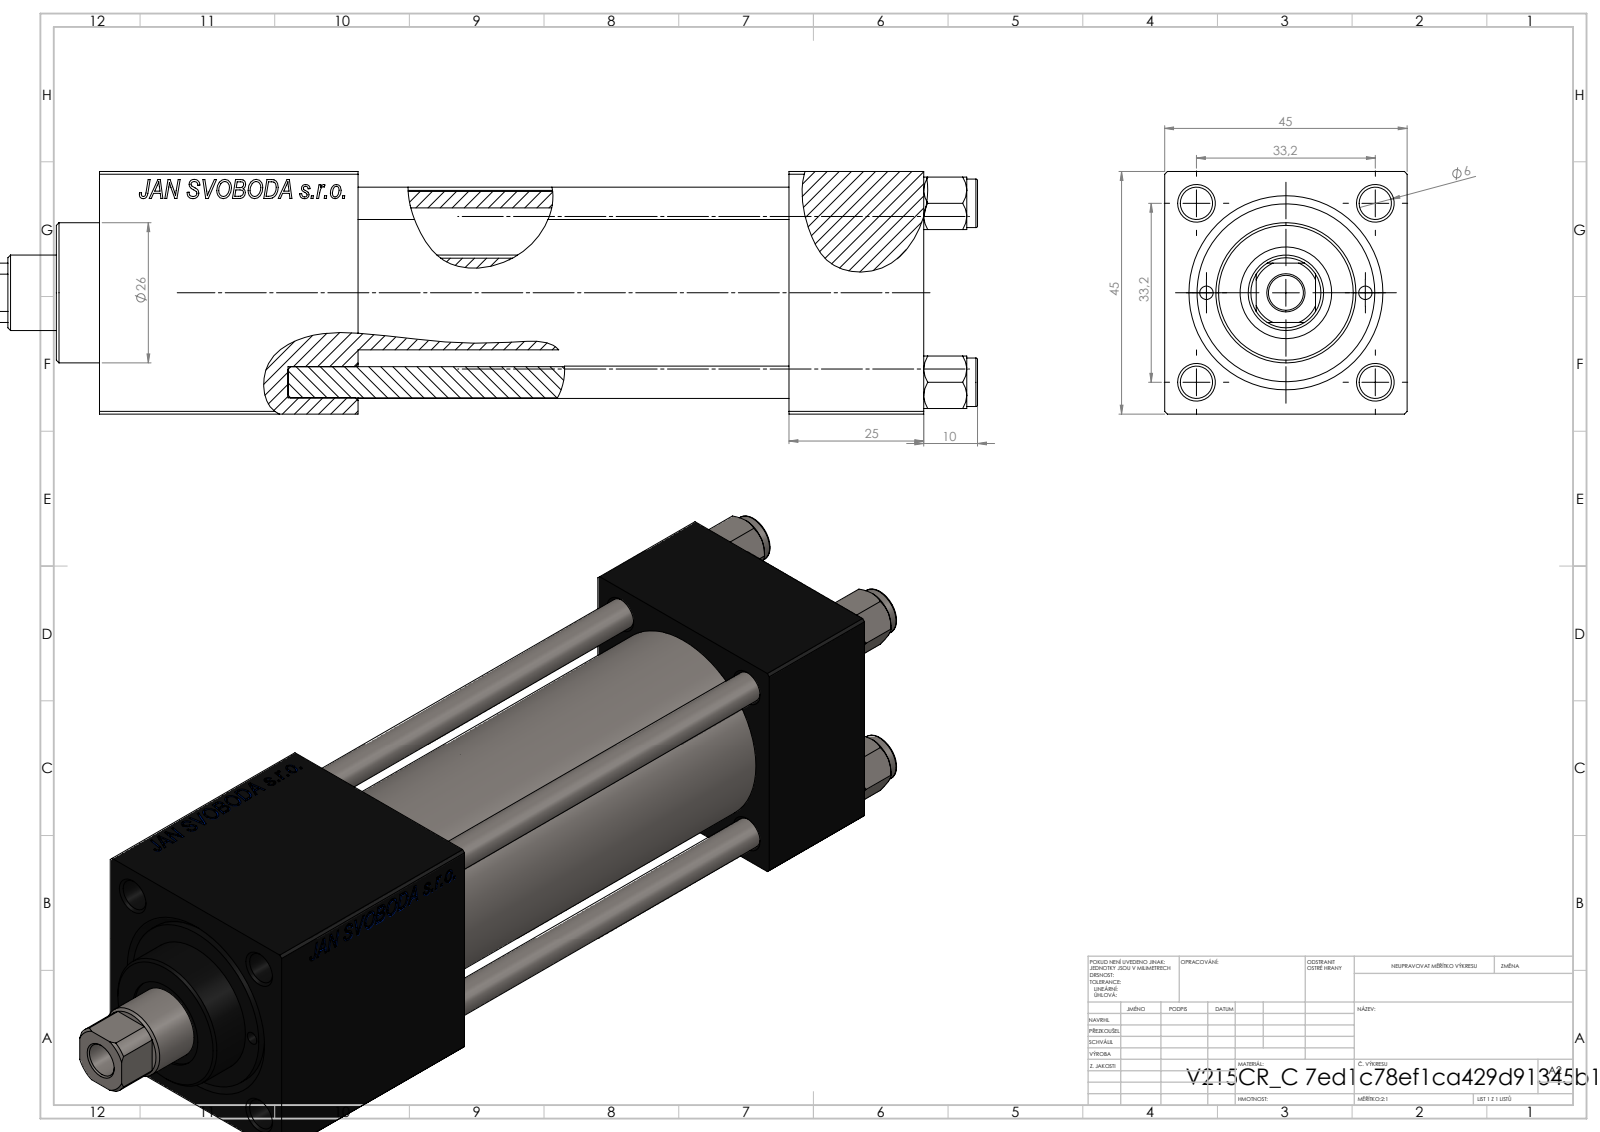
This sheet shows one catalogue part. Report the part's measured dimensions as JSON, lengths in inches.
{"part_name": "V215CR_C_Body; NUT_M5_C; V215CR_VCP_C; V215CR_C_TYCINKA (+1 more)", "step_written_by": "SolidWorks 2019 (CONFIG_CONTROL_DESIGN)", "units": "inches", "bodies": {"solids": 11, "faces": 1153, "planar": 527, "cylindrical": 90, "other": 536}, "overall_size": [7.402, 1.772, 1.772], "volume_in3": 12.92, "surface_area_in2": 119.9, "round_holes": [[0.236, 4], [0.098, 2], [0.276, 2], [0.518, 2], [0.787, 2], [0.256, 1], [0.551, 1], [0.669, 1], [0.945, 1], [1.26, 1], [1.299, 1]], "round_bosses_or_shafts": [[0.354, 4], [1.496, 1], [1.024, 1]], "partial_cylinders_radius": [[0.256, 1]], "face_to_face_distances": [1.772, 0.984, 5.039, 6.024, 4.134, 3.15, 1.89, 4.894, 3.909, 0.76], "hole_center_spacings": [0.657, 0.924, 1.307, 1.396, 0.581, 1.848, 1.161, 4.154]}
